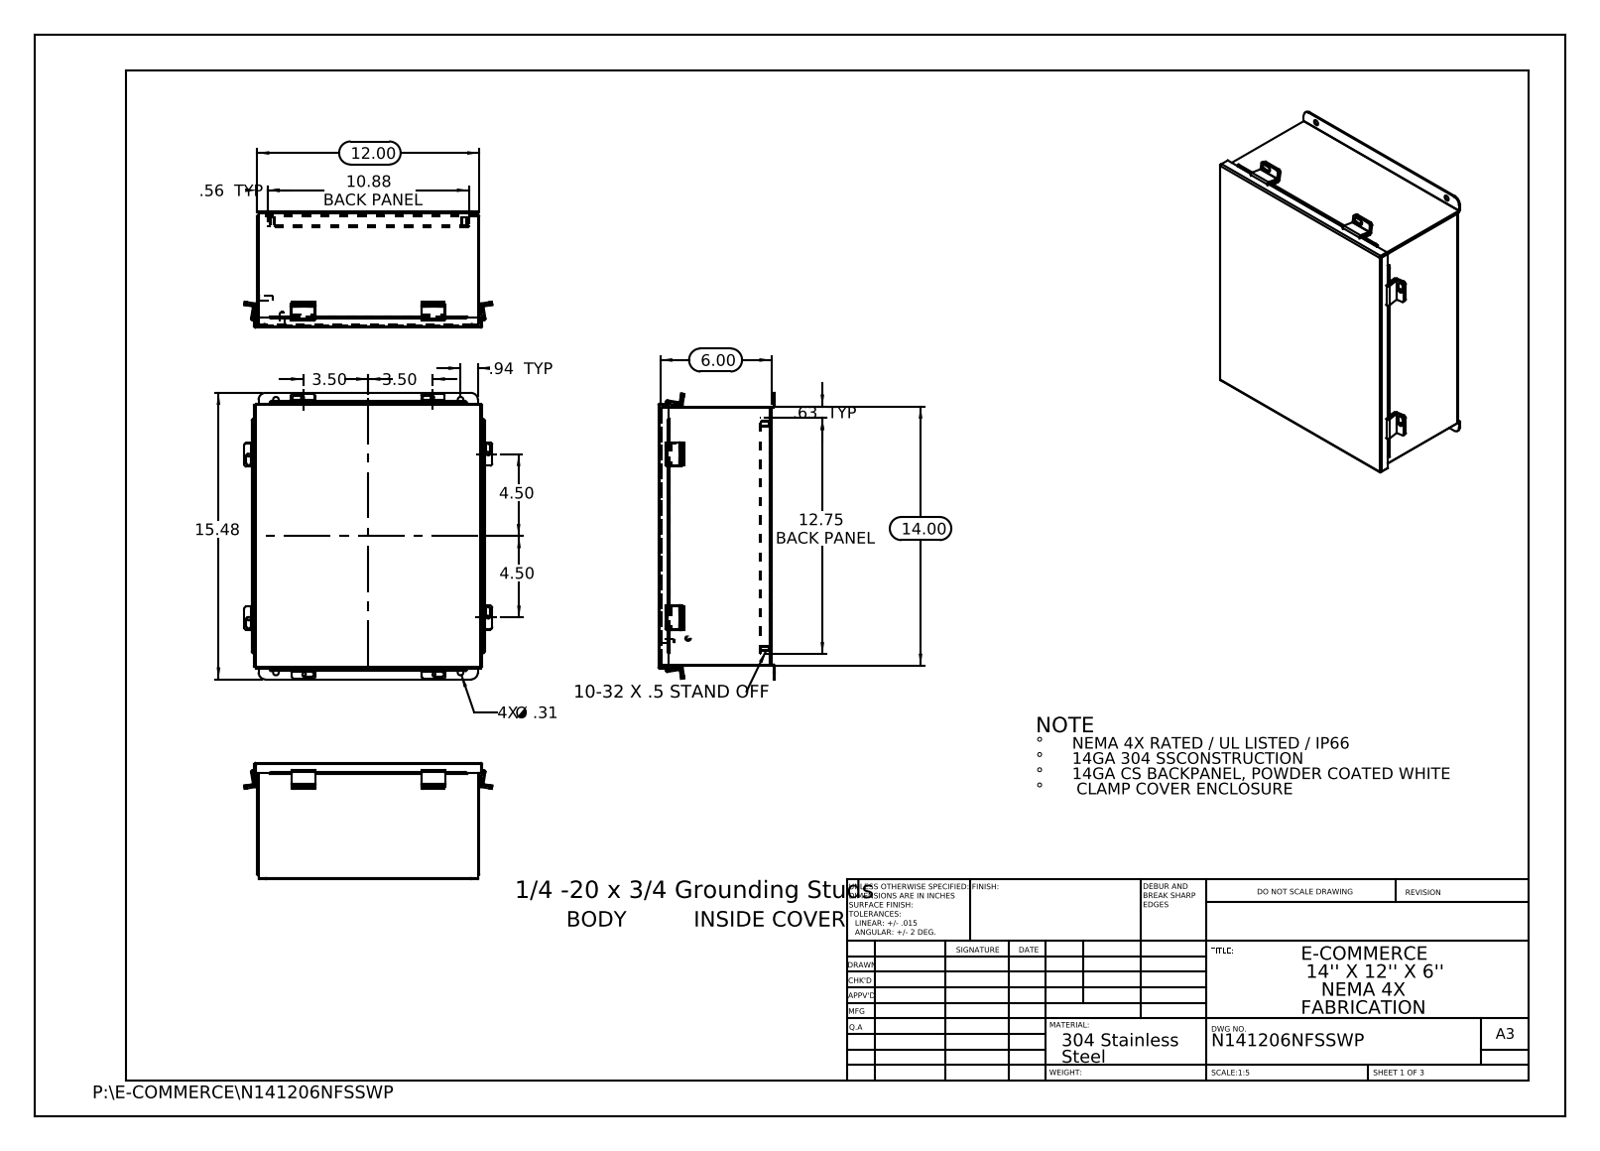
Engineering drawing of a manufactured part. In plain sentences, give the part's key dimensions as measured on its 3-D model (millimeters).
The part is named "N141206NFSSWP JIC Bottom; N141206NFSSWP HW-CD-S-25020-034; HW-CLH-JH-20154; N141206NFSSWP JIC Enclosure Template (+8 more)". Its 3-D file was written by "SolidWorks 2013 (CONFIG_CONTROL_DESIGN)". It is 27 solids with 806 faces: 519 planar, 267 cylindrical and 20 other. Overall it measures 393.1 by 332 by 162.3 millimeters. Its volume is 1 106 000 cubic millimeters and its surface area 1 186 000 square millimeters. Round holes: 10 of diameter 6.4, 4 of diameter 4.7, 4 of diameter 7.9, 1 of diameter 3.2, 1 of diameter 3.2, 1 of diameter 9.5, 1 of diameter 9.5. Round bosses or shafts: 4 of diameter 8, 2 of diameter 8, 2 of diameter 6, 1 of diameter 6.9, 1 of diameter 6.4. Partial cylindrical surfaces (rounded edges, fillets, slot ends): 21 of radius 3.2, 13 of radius 0.3, 12 of radius 0.2, 12 of radius 2.2, 12 of radius 3.4, 6 of radius 2.1, 6 of radius 2.5, 4 of radius 9.5. The main face-to-face distances are 1.9, 155.7, 153.7, 157.6, 302.9, 353.7, 1.9, 14.6, 12.7, 141. The hole center spacings are 33.4, 260.6, 341.1, 427.9, 177.8, 253.4, 263.5, 308.
